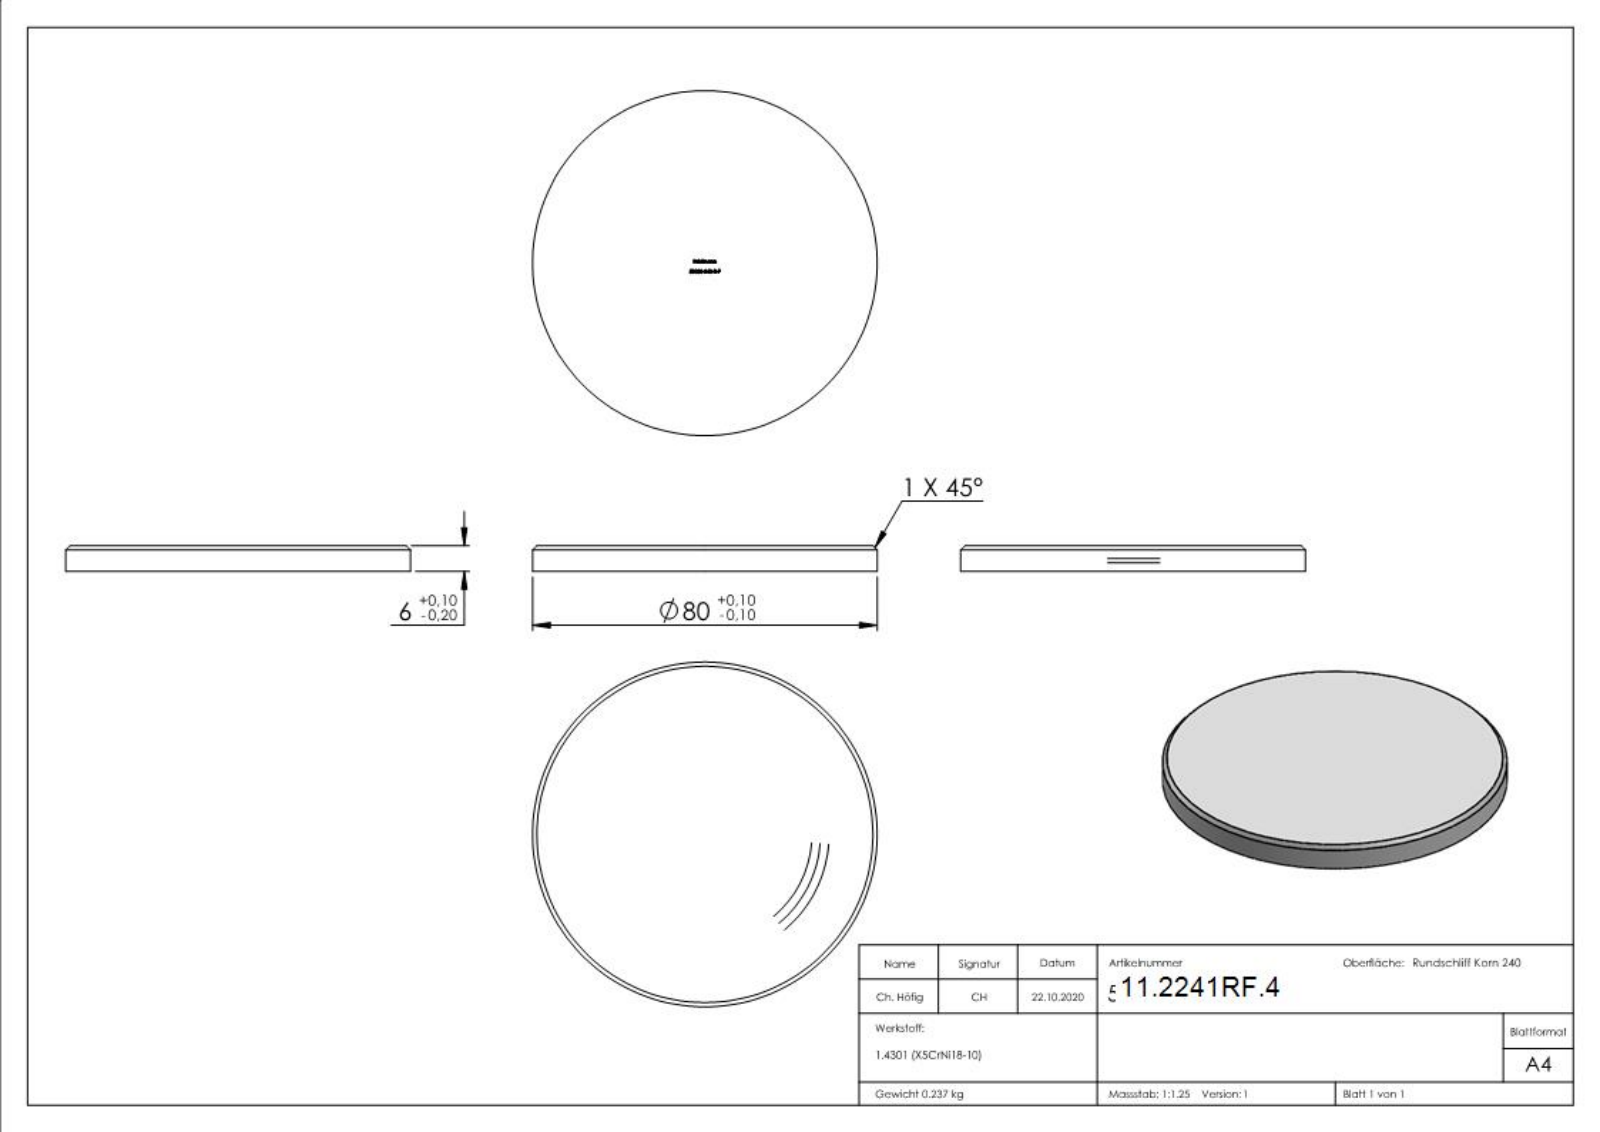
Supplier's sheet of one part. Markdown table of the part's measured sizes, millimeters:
| quantity | value |
| --- | --- |
| part name | 53080-240-R-F |
| STEP written by | SolidWorks 2018 (CONFIG_CONTROL_DESIGN) |
| units | millimeters |
| bodies | 1 solid, 277 faces (148 planar, 2 cylindrical, 127 other) |
| overall size | 80 × 80 × 6 |
| volume | 30 034 mm³ |
| surface area | 11 419 mm² |
| round bosses / shafts (diameter × count) | 80 × 1 |
| main face-to-face distances | 6, 5.9, 2.32, 1.21, 3.49, 0.79, 1.78, 2.24, 2.2, 0.83 |
